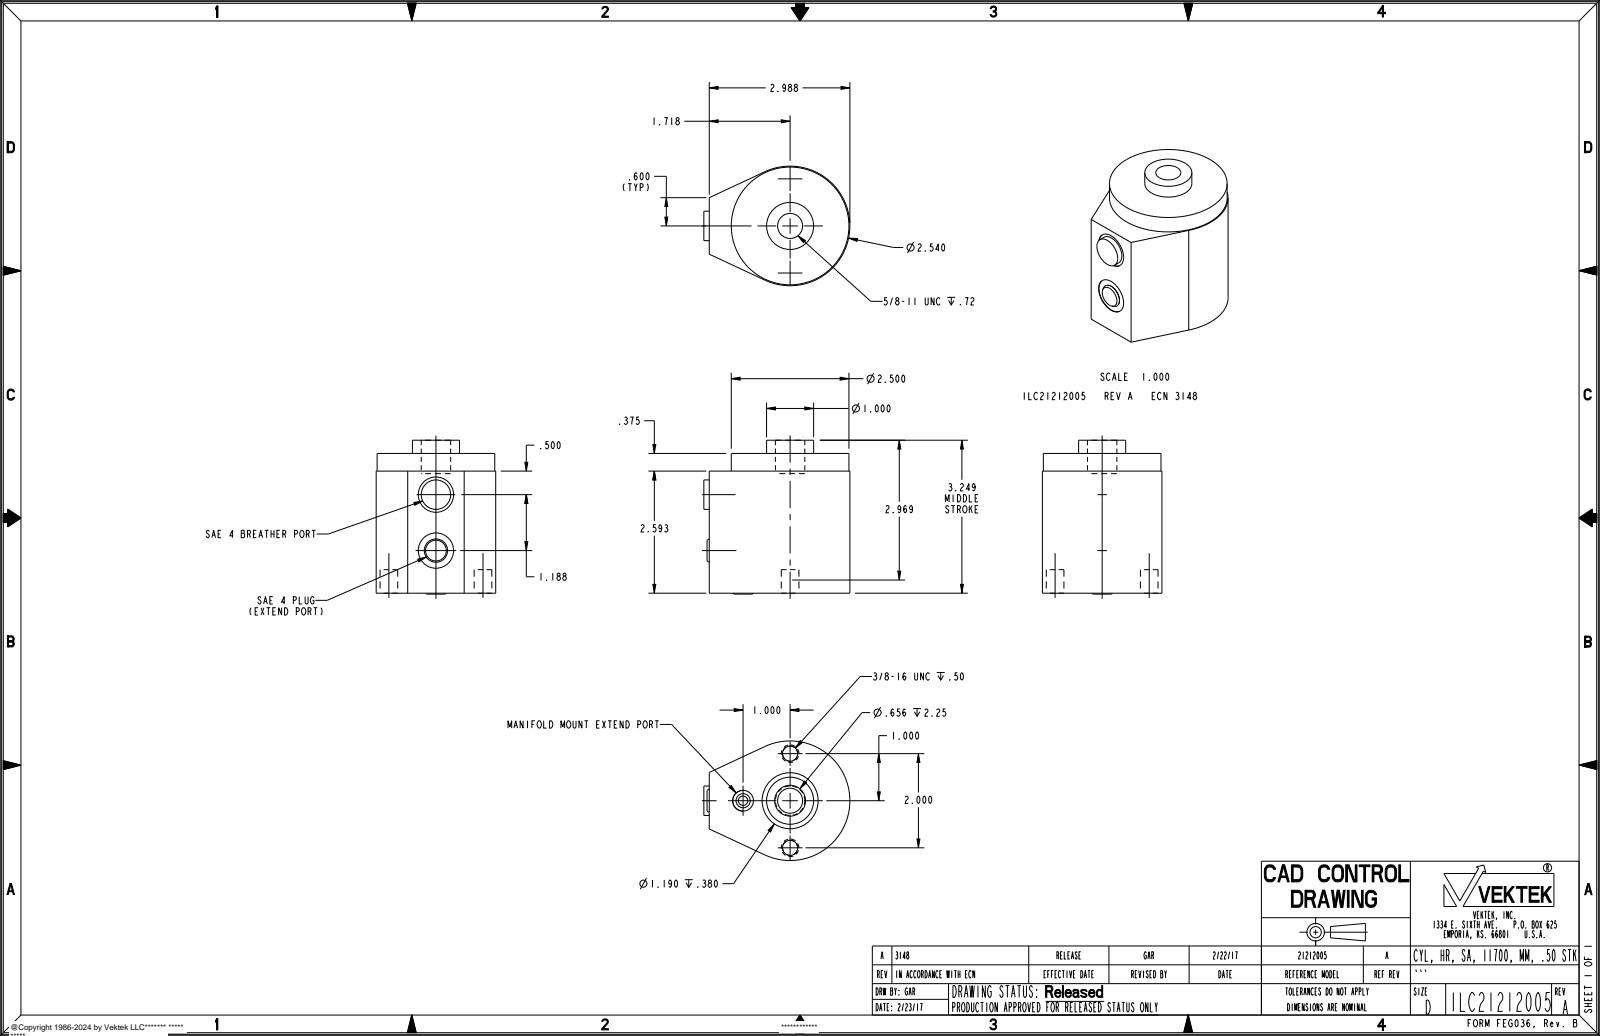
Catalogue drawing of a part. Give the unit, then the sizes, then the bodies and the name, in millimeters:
Units: millimetres
Overall size (bounding box): 83 × 78.8 × 64.5
Round holes (diameter × count): ⌀8.2 ×2, ⌀10 ×2, ⌀19.1 ×2, ⌀5.1 ×1, ⌀11.2 ×1, ⌀13.5 ×1, ⌀16.7 ×1, ⌀30.2 ×1
Round bosses / shafts (diameter × count): ⌀15.9 ×2, ⌀9.5 ×2, ⌀63.5 ×1, ⌀25.4 ×1
Partial cylindrical surfaces — rounded edges, fillets, slot ends (radius × count): R32.3 ×1
Main face-to-face distances: 75.4, 65.9, 9.5, 7.1, 82.5, 16.7, 7.1, 58.8, 68.3, 75.4
Hole centre spacings: 25.4, 35.9, 30.2, 50.8
Volume: 260 100 mm³ · Surface area: 34 430 mm²
Bodies: 2 solids, 75 faces (22 planar, 37 cylindrical, 16 other)
Part name (STEP PRODUCT): ILC21212005
STEP written by: PRO/ENGINEER BY PARAMETRIC TECHNOLOGY CORPORATION, 2013320 (AUTOMOTIVE_DESIGN)
